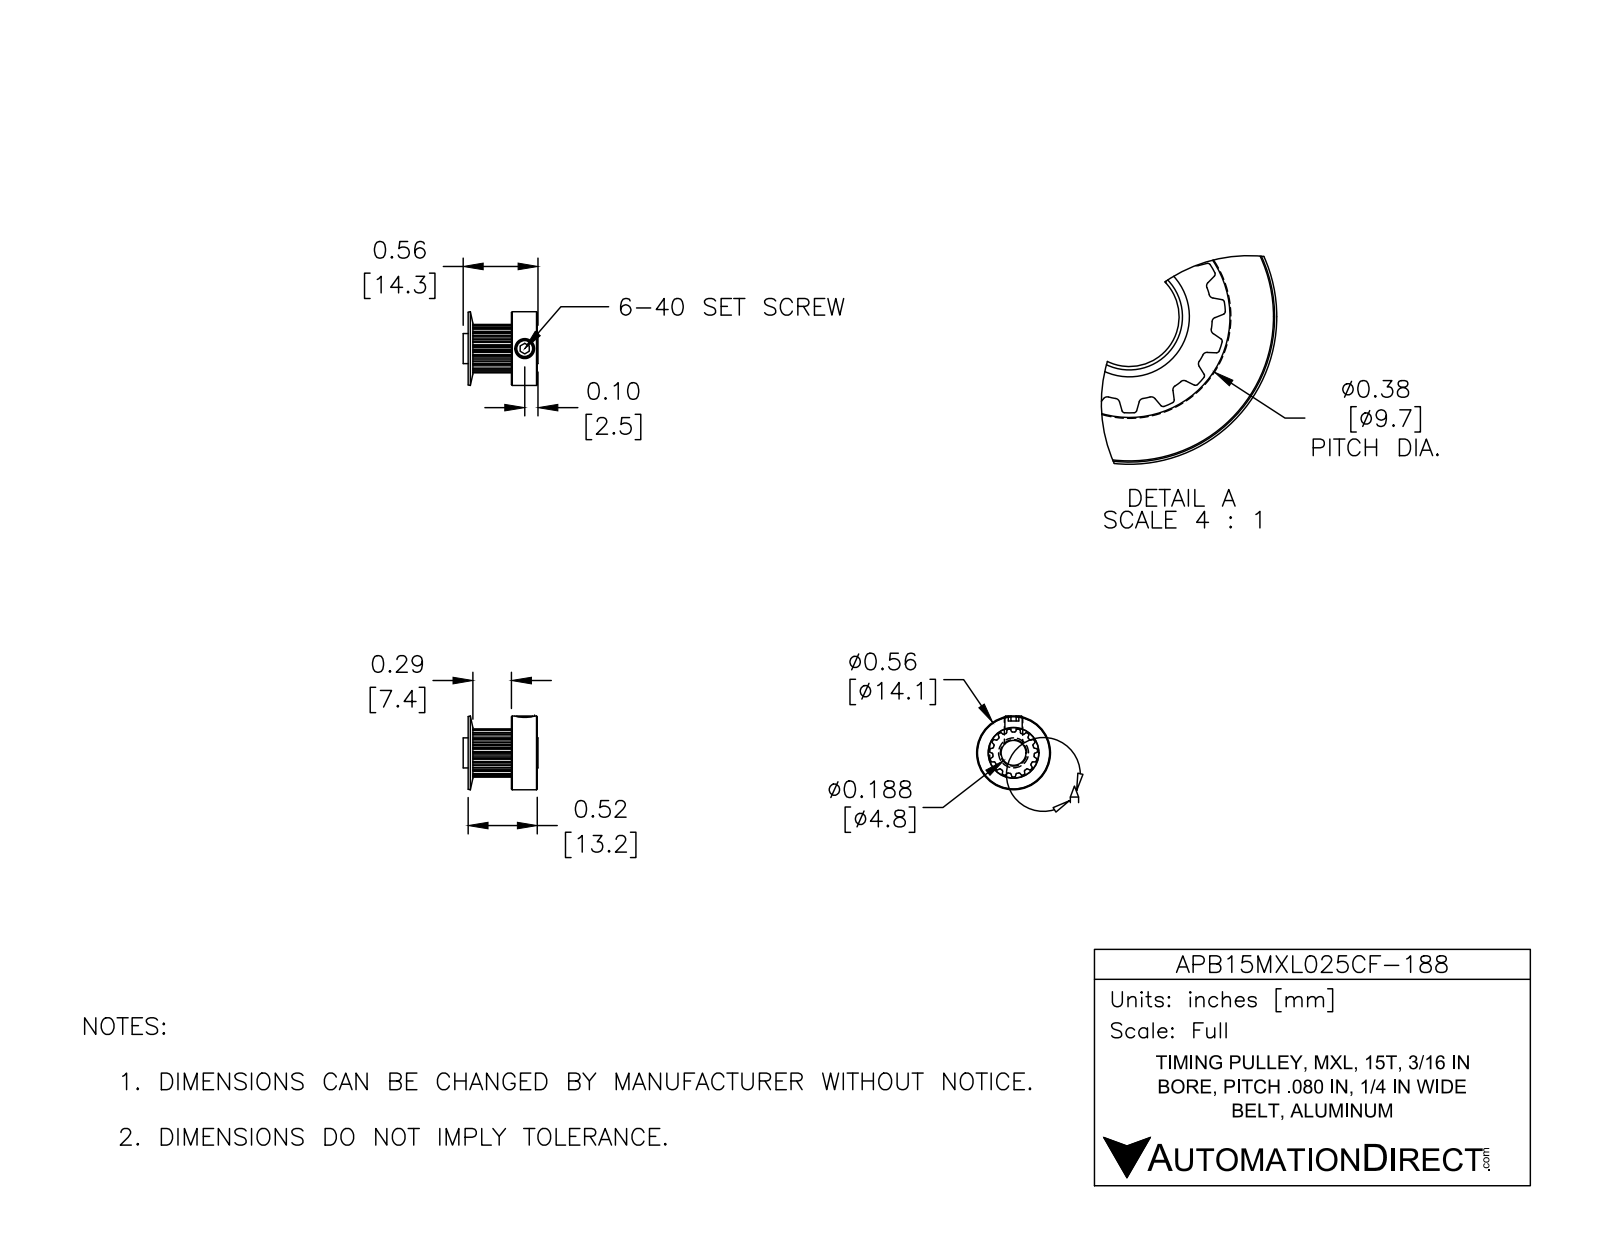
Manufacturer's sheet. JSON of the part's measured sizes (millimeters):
{"part_name": "APB15MXL025CF-188", "step_written_by": "SolidWorks 2016 (AUTOMOTIVE_DESIGN)", "units": "millimeters", "bodies": {"solids": 2, "faces": 176, "planar": 45, "cylindrical": 113, "other": 18}, "overall_size": [14.3, 14.1, 14.1], "volume_mm3": 1000, "surface_area_mm2": 1302, "round_holes": [[3.5, 1], [4.7, 1]], "round_bosses_or_shafts": [[14.1, 1], [5.7, 1], [3.3, 1]], "partial_cylinders_radius": [[0.1, 30], [0.2, 30], [4, 1], [4.6, 1]], "face_to_face_distances": [4.9, 7.8, 12.8, 0.5, 7.4, 12.3, 1.4, 1.9, 9.2, 14.1]}
